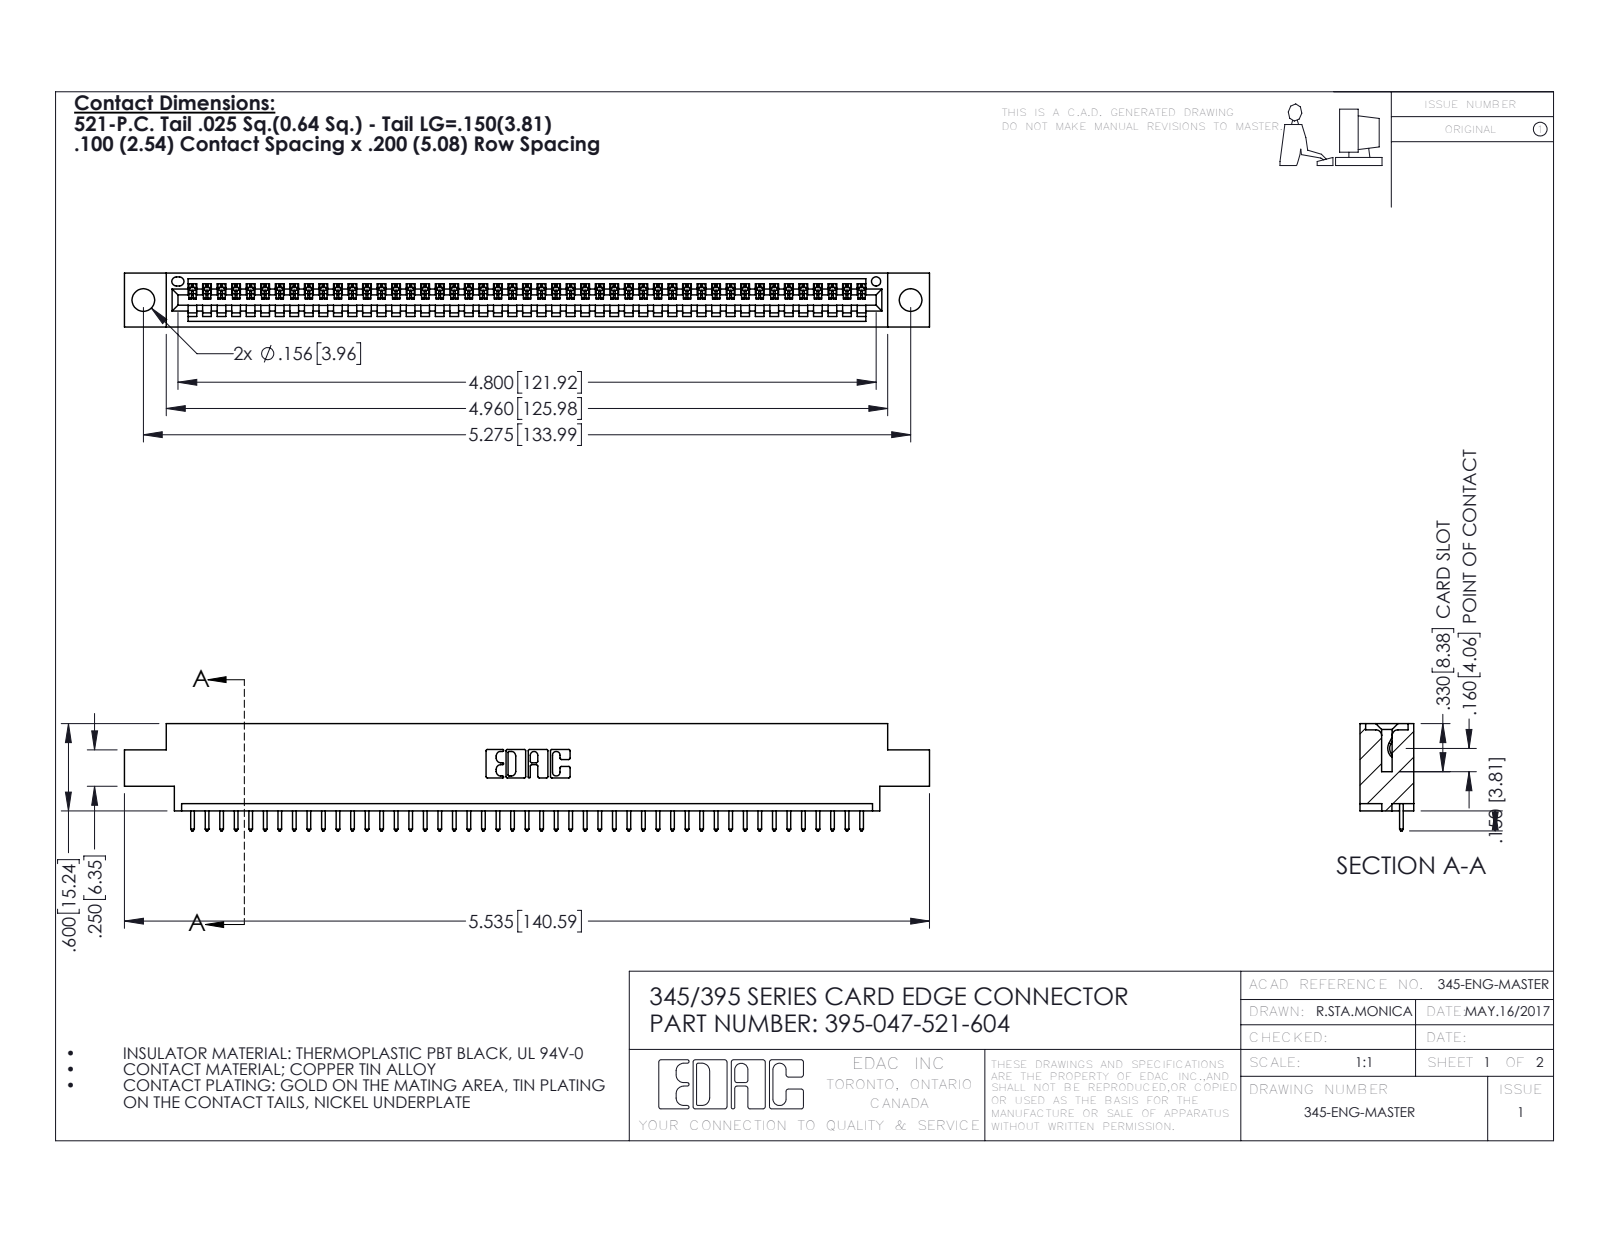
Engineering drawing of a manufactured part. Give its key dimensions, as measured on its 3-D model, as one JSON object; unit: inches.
{"part_name": "345 Part_0.170 Offset - 0.156 Dia-TH; 345-292-001_345-293-121; 395-047-521-604", "step_written_by": "SolidWorks 2016 (CONFIG_CONTROL_DESIGN)", "units": "inches", "bodies": {"solids": 48, "faces": 2856, "planar": 1964, "cylindrical": 892, "other": 0}, "overall_size": [5.535, 0.737, 0.37], "volume_in3": 0.797, "surface_area_in2": 26.09, "round_holes": [[0.156, 2], [0.064, 1]], "partial_cylinders_radius": [[0.006, 94], [0.01, 94], [0.01, 22], [0.007, 6], [0.031, 6], [0.026, 3], [0.031, 2], [0.04, 2]], "face_to_face_distances": [0.298, 0.072, 0.37, 0.2, 0.098, 0.272, 0.025, 0.225, 0.175, 0.149], "hole_center_spacings": [0.27, 5.039, 5.275]}
